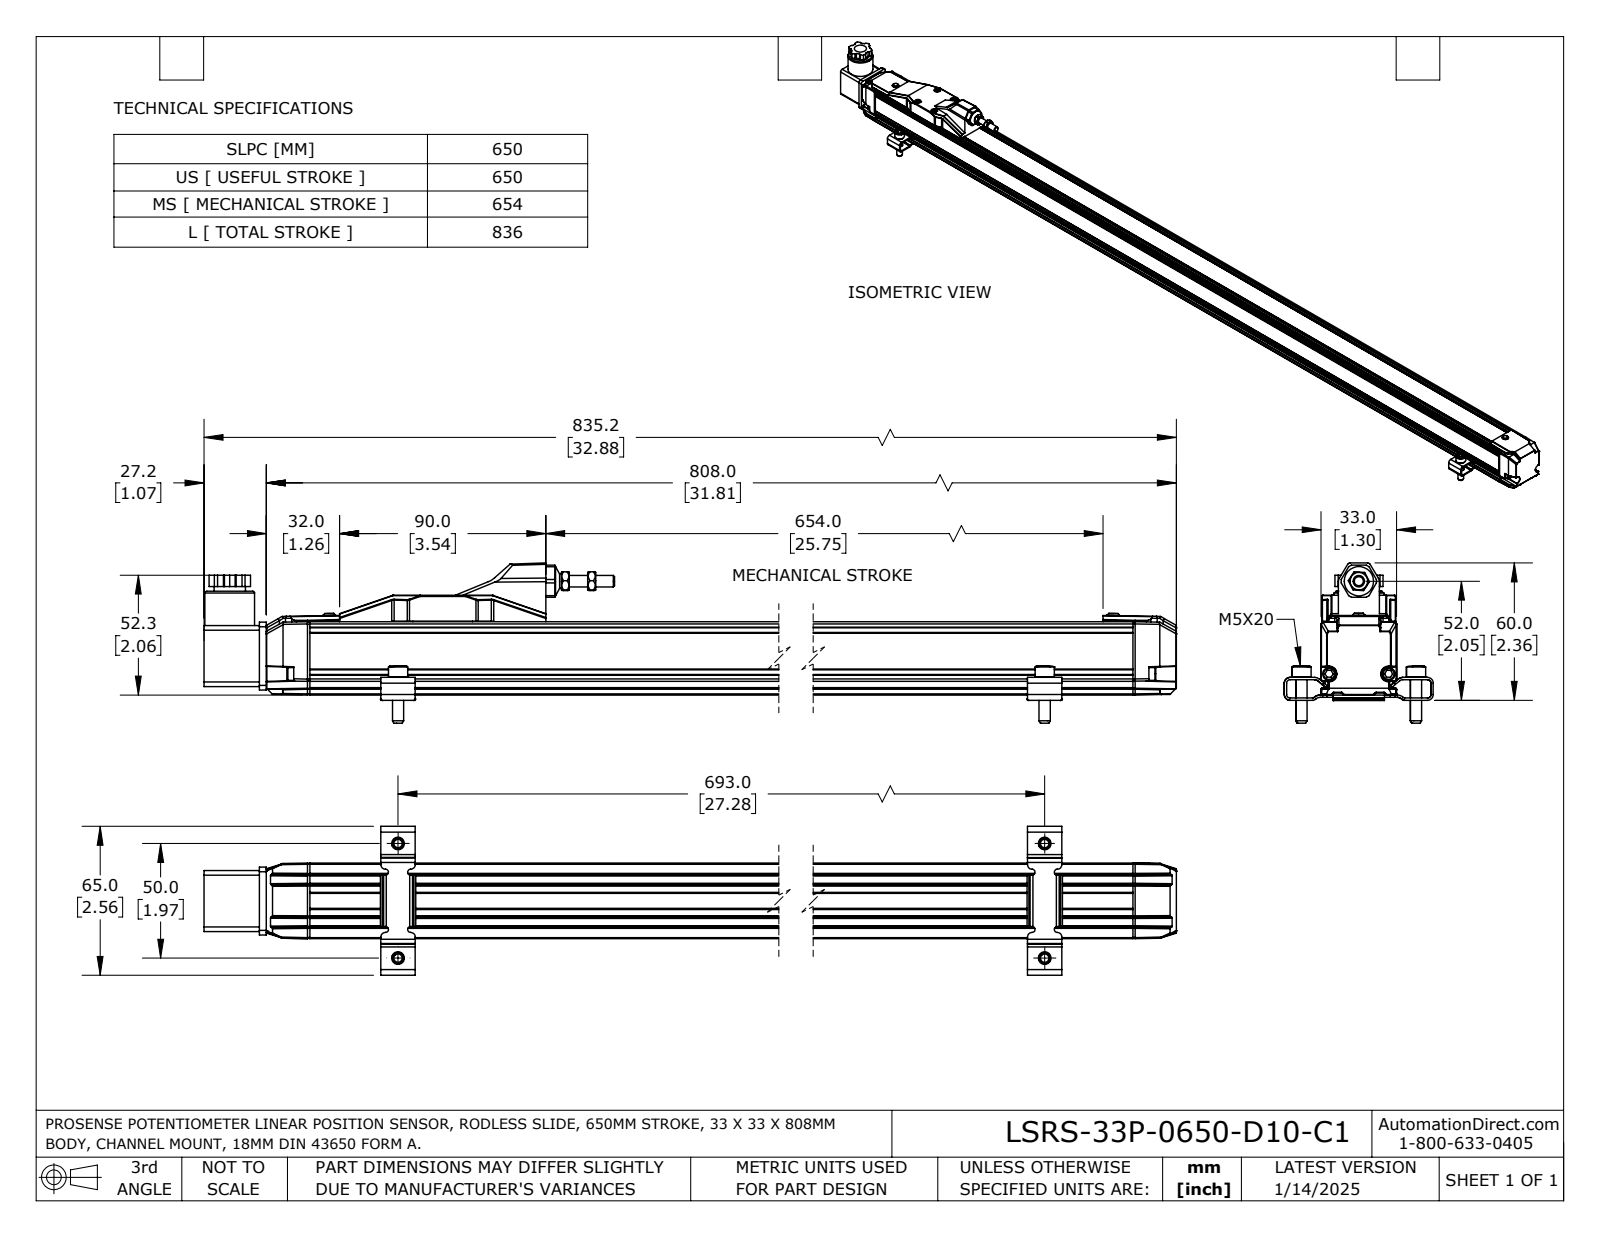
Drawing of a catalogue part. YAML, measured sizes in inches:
part_name: "LSRS-33P-0650-D10-C1"
step_written_by: "SolidWorks 2023 (AUTOMOTIVE_DESIGN)"
units: inches
bodies: {solids: 11, faces: 1314, planar: 823, cylindrical: 359, other: 132}
overall_size: [32.882, 2.754, 2.559]
volume: 48.37
surface_area: 292.8
round_holes:
  - {diameter: 0.185, count: 4}
  - {diameter: 0.217, count: 4}
  - {diameter: 0.106, count: 2}
  - {diameter: 0.13, count: 2}
  - {diameter: 0.157, count: 1}
  - {diameter: 0.197, count: 1}
  - {diameter: 0.209, count: 1}
  - {diameter: 0.232, count: 1}
  - {diameter: 0.236, count: 1}
  - {diameter: 0.276, count: 1}
  - {diameter: 0.394, count: 1}
  - {diameter: 0.413, count: 1}
round_bosses_or_shafts:
  - {diameter: 0.331, count: 4}
  - {diameter: 0.193, count: 4}
  - {diameter: 0.181, count: 4}
  - {diameter: 0.22, count: 2}
  - {diameter: 0.217, count: 2}
  - {diameter: 0.118, count: 2}
  - {diameter: 0.113, count: 2}
  - {diameter: 0.113, count: 2}
partial_cylinders:
  - {radius: 0.02, count: 78}
  - {radius: 0.008, count: 62}
  - {radius: 0.079, count: 44}
  - {radius: 0.118, count: 26}
  - {radius: 0.039, count: 10}
  - {radius: 0.051, count: 8}
  - {radius: 0.059, count: 8}
  - {radius: 0.157, count: 8}
face_to_face_distances: [1.299, 0.118, 1.244, 1.167, 0.237, 1.007, 0.035, 0.014, 1.285, 0.443]
hole_center_spacings: [0.597, 0.787, 0.933, 1.221, 1.286, 1.673, 1.969, 26.127]
